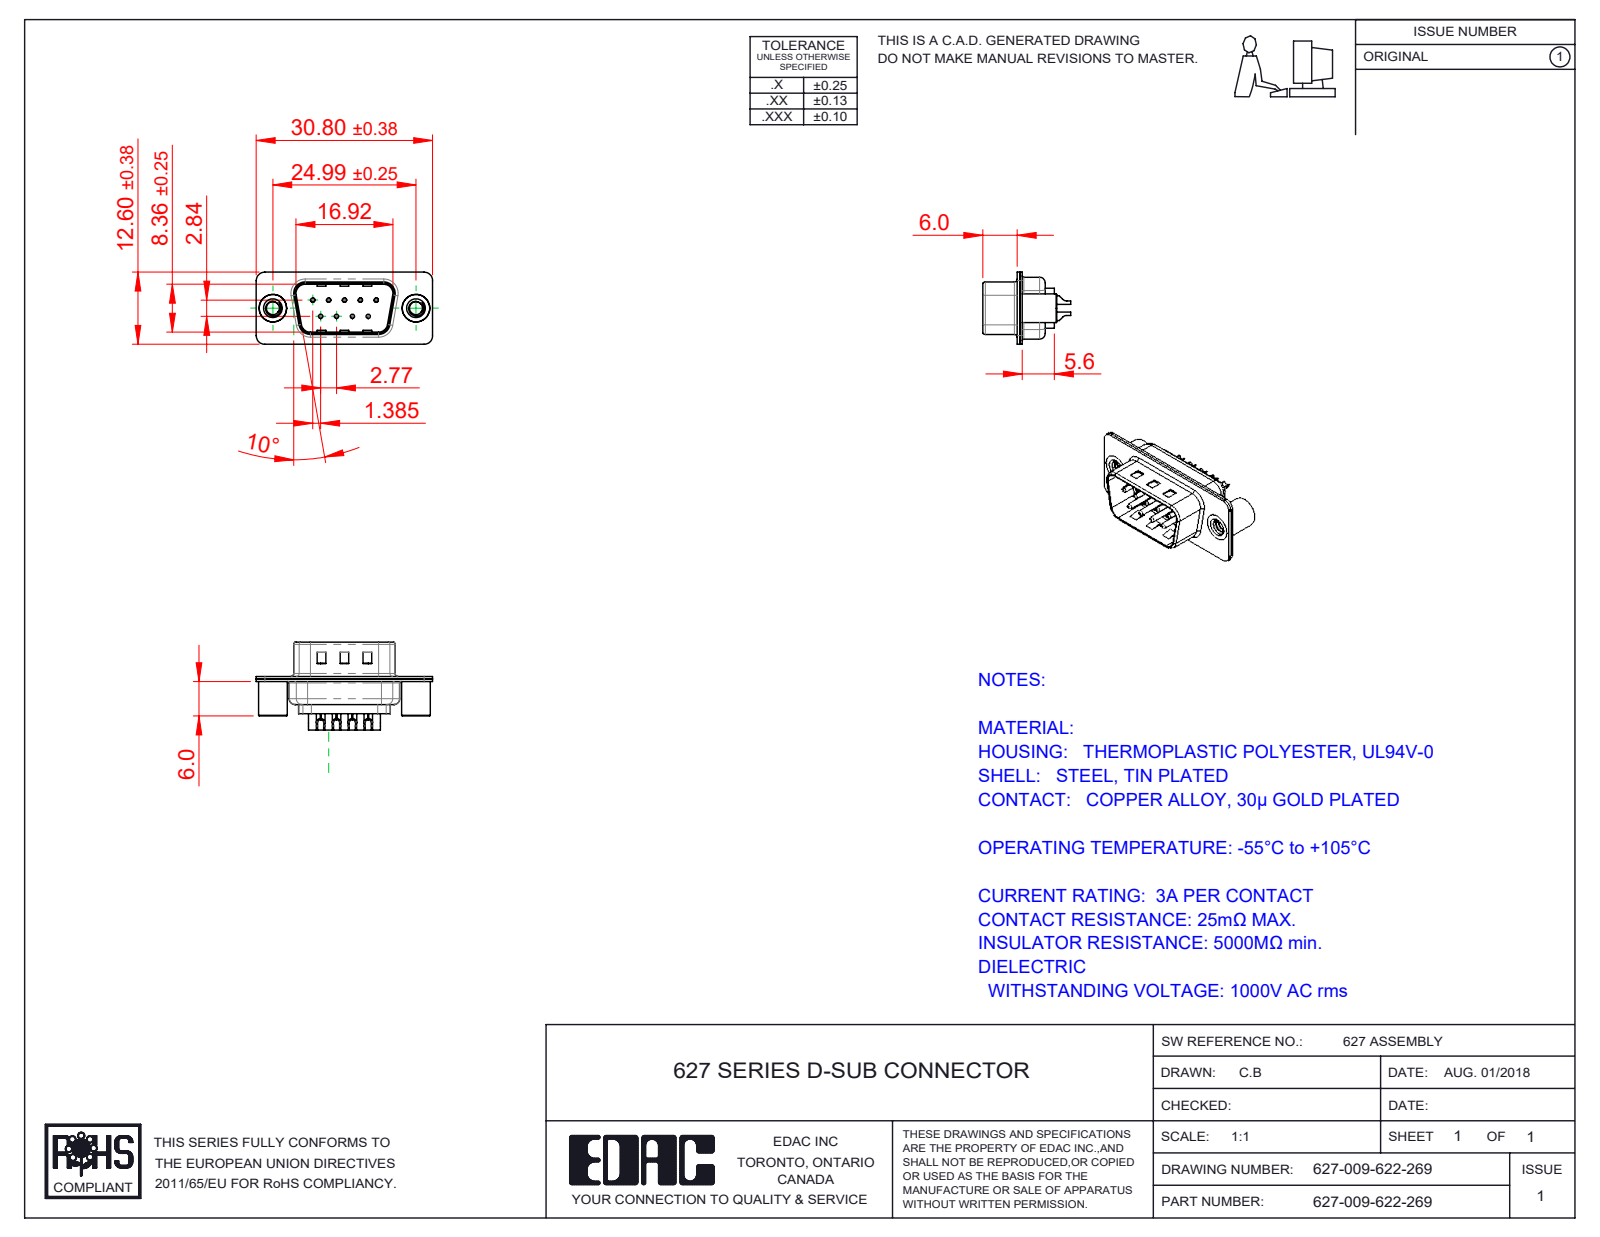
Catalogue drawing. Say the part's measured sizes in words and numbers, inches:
The part is named "627 4-40 Threaded Standoff BS; 627 Housing_09 LP; 627 Shell Rear_09 Contacts; 627-009-622-069 (+3 more)". Its 3-D file was written by "SolidWorks 2020 (CONFIG_CONTROL_DESIGN)". It is 14 solids with 902 faces: 233 planar, 410 cylindrical and 259 other. Overall it measures 1.213 by 0.604 by 0.496 inches. Its volume is 0.086 cubic inches and its surface area 6.422 square inches. Round holes: 9 of diameter 0.014, 9 of diameter 0.043, 9 of diameter 0.063, 2 of diameter 0.089, 2 of diameter 0.157, 2 of diameter 0.189. Round bosses or shafts: 9 of diameter 0.079, 9 of diameter 0.059, 9 of diameter 0.03, 2 of diameter 0.197, 2 of diameter 0.193. Partial cylindrical surfaces (rounded edges, fillets, slot ends): 18 of radius 0.059, 12 of radius 0.079, 8 of radius 0.02, 8 of radius 0.063, 6 of radius 0.039, 4 of radius 0.01, 4 of radius 0.024, 4 of radius 0.026. The main face-to-face distances are 0.018, 0.016, 0.035, 0.032, 0.377, 0.055, 0.345, 0.256, 0.02, 0.059. The hole center spacings are 0.124, 0.109, 0.218, 0.198, 0.198, 0.327, 0.294, 0.295.
